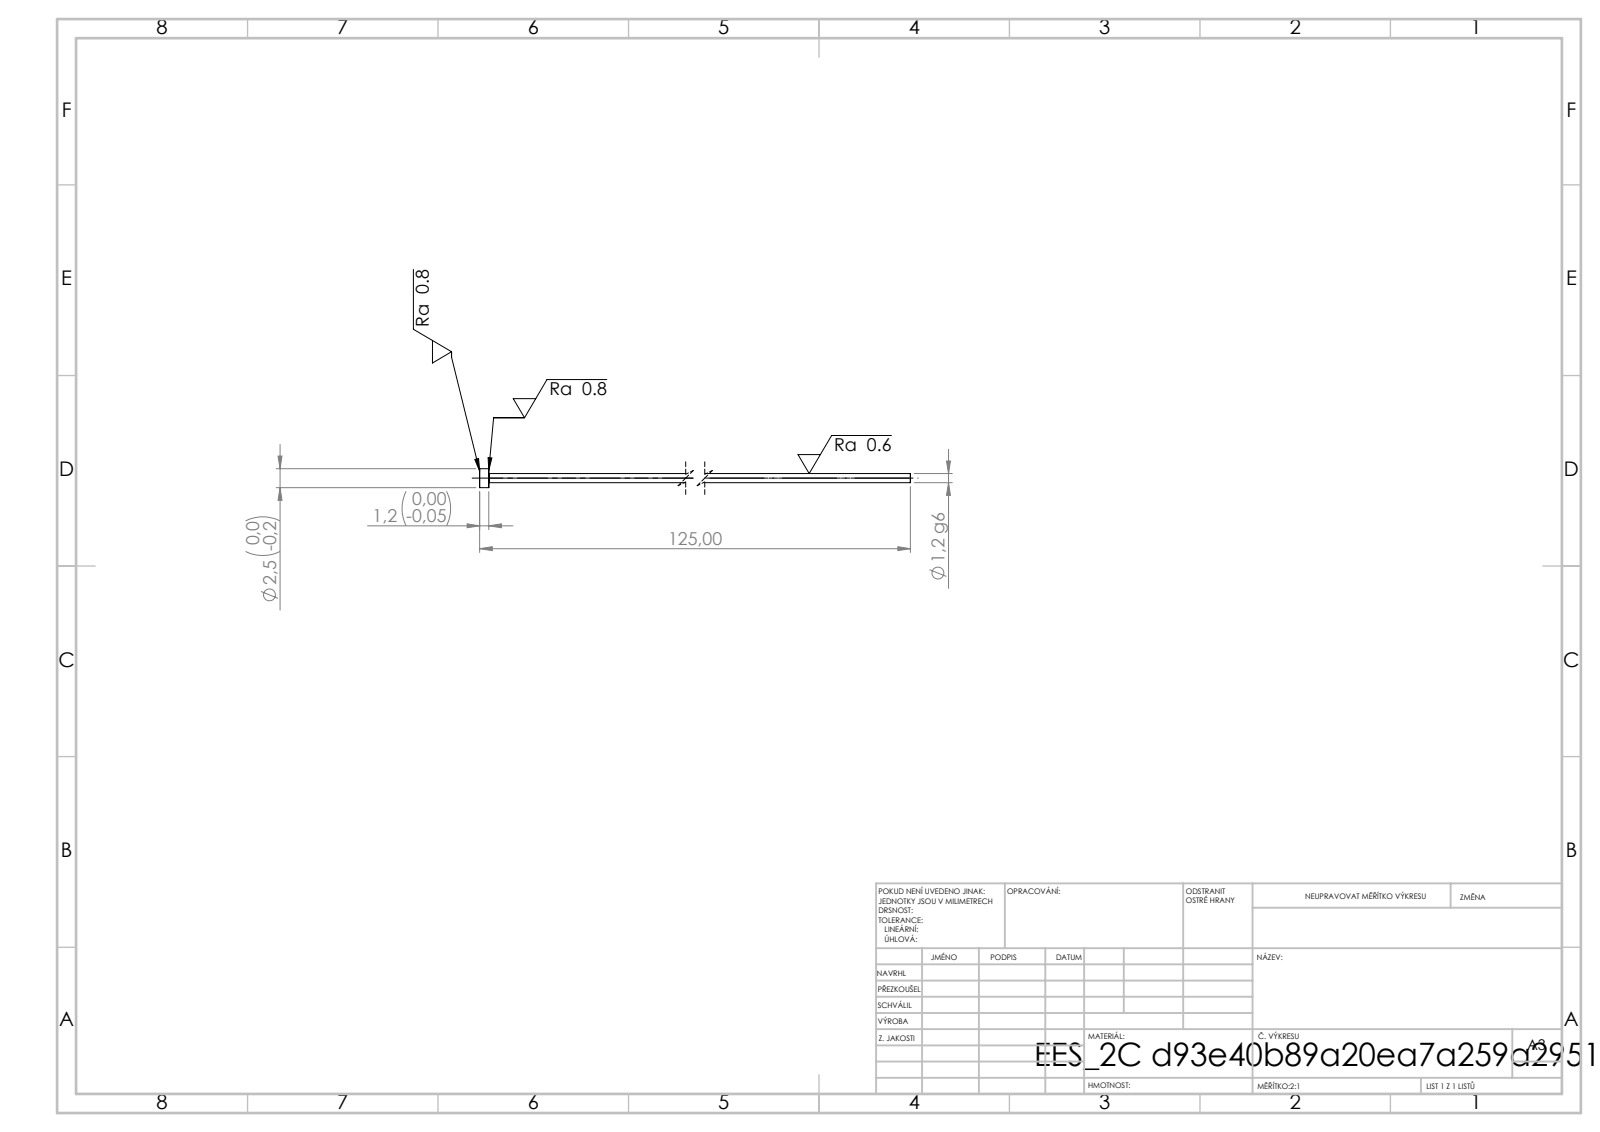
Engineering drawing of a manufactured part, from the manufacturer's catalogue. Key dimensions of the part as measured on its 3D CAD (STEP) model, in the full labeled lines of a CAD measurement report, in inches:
STEP written by: SolidWorks 2019 (CONFIG_CONTROL_DESIGN)
Units: inches
Bodies: 1 solid, 7 faces (3 planar, 4 cylindrical, 0 other)
Overall size (bounding box): 4.921 × 0.098 × 0.098
Volume: 0.009 in³ · Surface area: 0.753 in²
Round bosses / shafts (diameter × count): ⌀0.098 ×1, ⌀0.047 ×1
Main face-to-face distances: 0.047, 4.921, 4.874
